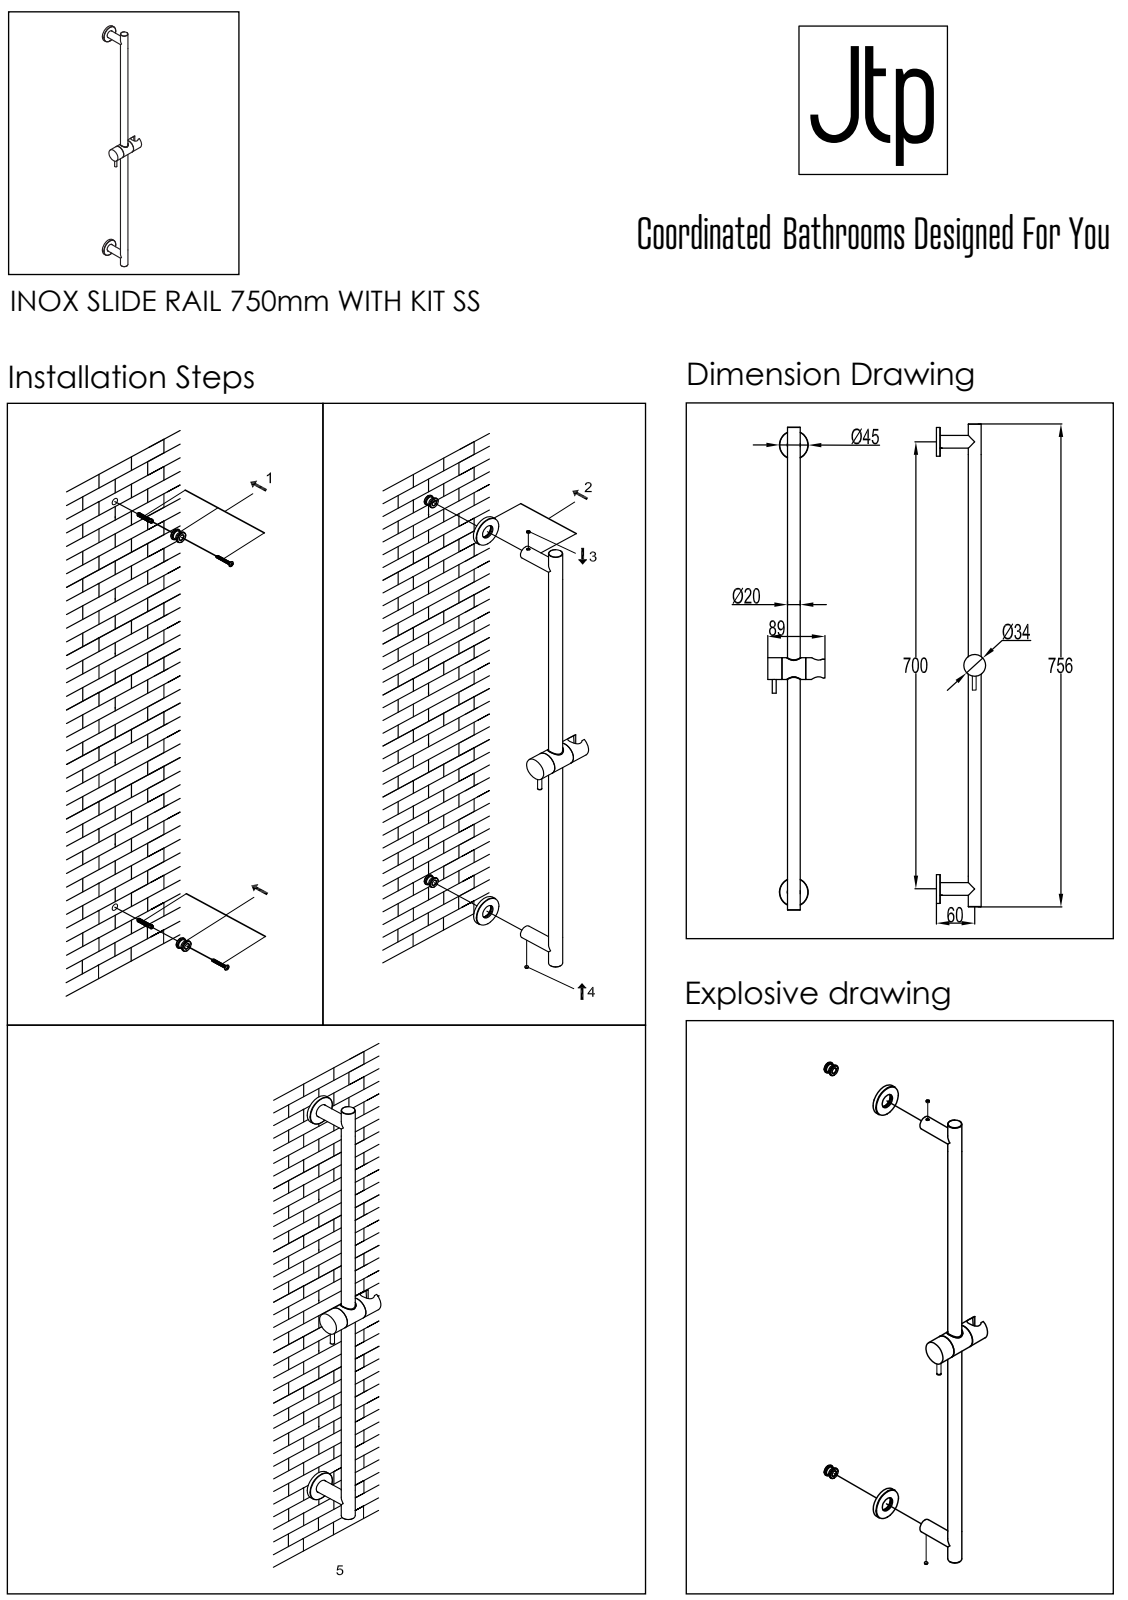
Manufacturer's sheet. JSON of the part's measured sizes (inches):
{"part_name": "178", "step_written_by": "PRO/ENGINEER BY PARAMETRIC TECHNOLOGY CORPORATION, 2012130 (CONFIG_CONTROL_DESIGN)", "units": "inches", "bodies": {"solids": 4, "faces": 550, "planar": 82, "cylindrical": 397, "other": 71}, "overall_size": [652, 101, 87], "volume_in3": 523373, "surface_area_in2": 111312, "round_holes": [[0.8, 50], [32.5, 2], [20.5, 1]], "round_bosses_or_shafts": [[2, 50], [52, 2], [32, 2], [28, 1], [25, 1], [21, 1], [19.2, 1], [15, 1]], "partial_cylinders_radius": [[0.5, 4], [16, 1]], "face_to_face_distances": [6, 75, 69, 28, 32, 87, 241, 213, 281.97, 309.97], "hole_center_spacings": [4, 8, 12, 16, 20, 24, 28, 32]}
